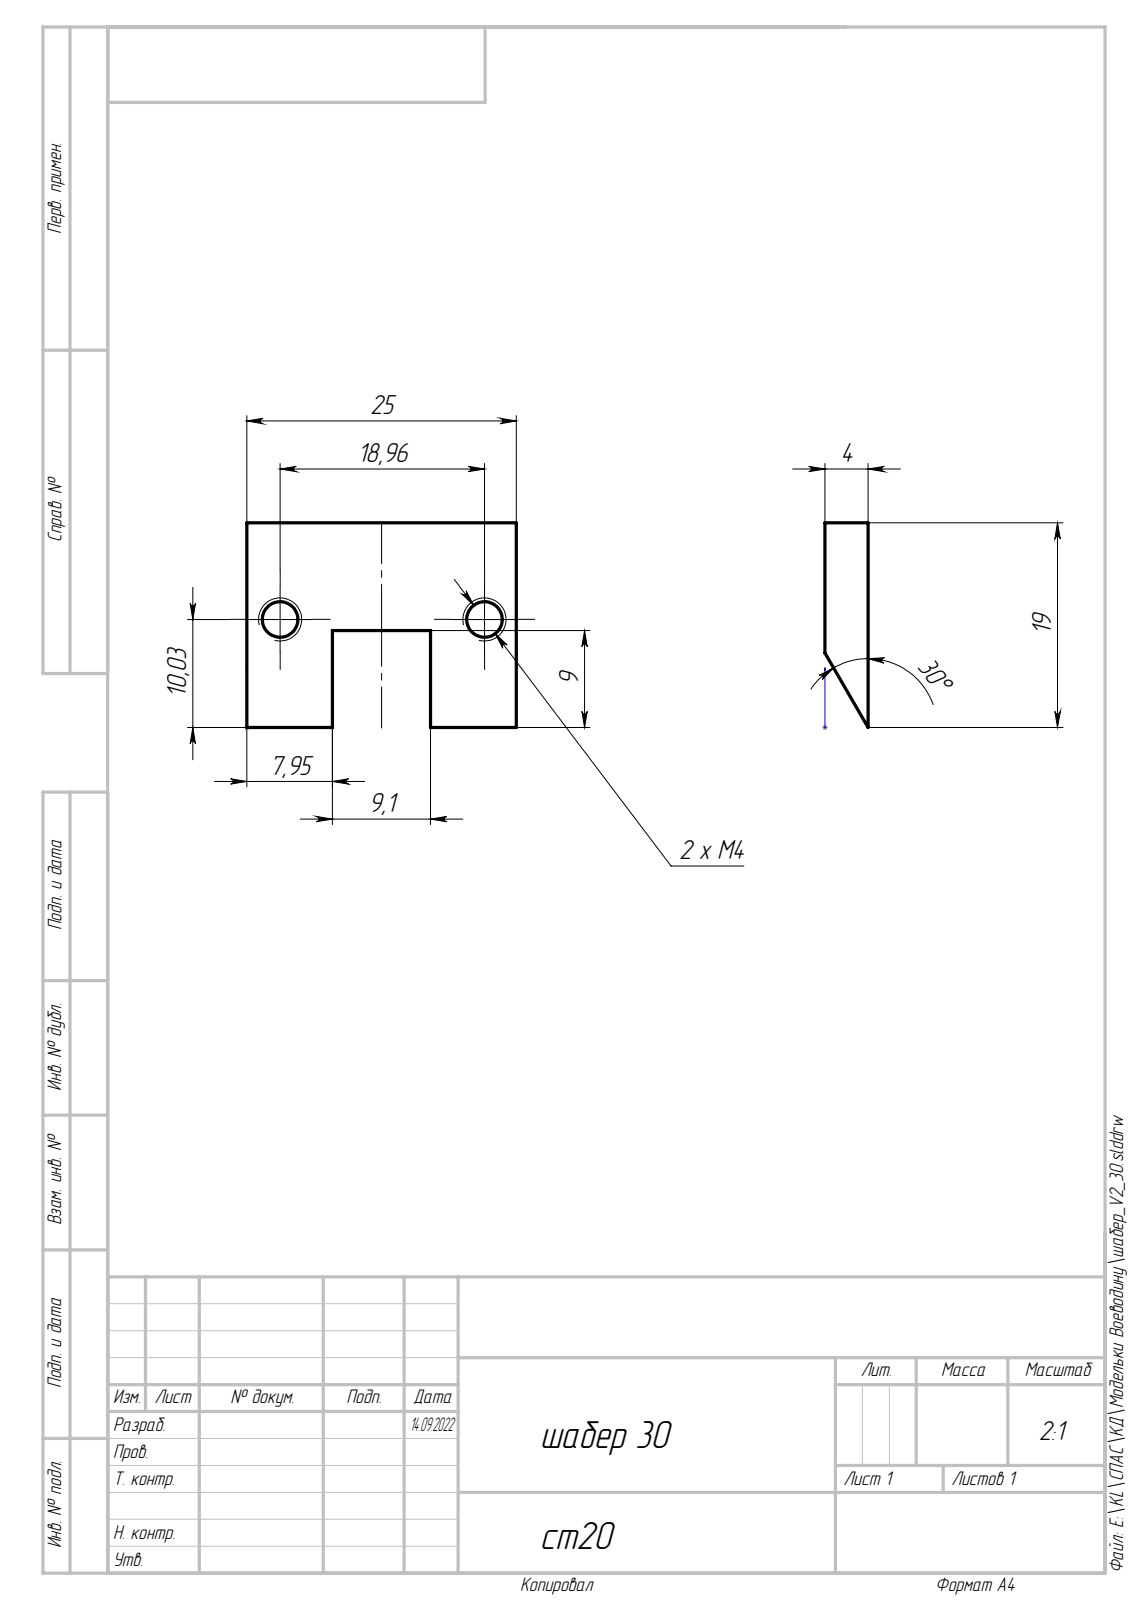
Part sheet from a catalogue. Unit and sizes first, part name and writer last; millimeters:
Units: millimetres
Overall size (bounding box): 25 × 19 × 4
Round holes (diameter × count): ⌀3.3 ×2
Main face-to-face distances: 4, 25, 7.95, 17.05, 10, 9.1
Hole centre spacings: 18.96
Volume: 1 284 mm³ · Surface area: 1 157 mm²
Bodies: 1 solid, 14 faces (10 planar, 4 cylindrical, 0 other)
Part name (STEP PRODUCT): шабер 30
STEP written by: SolidWorks 2021 (AUTOMOTIVE_DESIGN)
